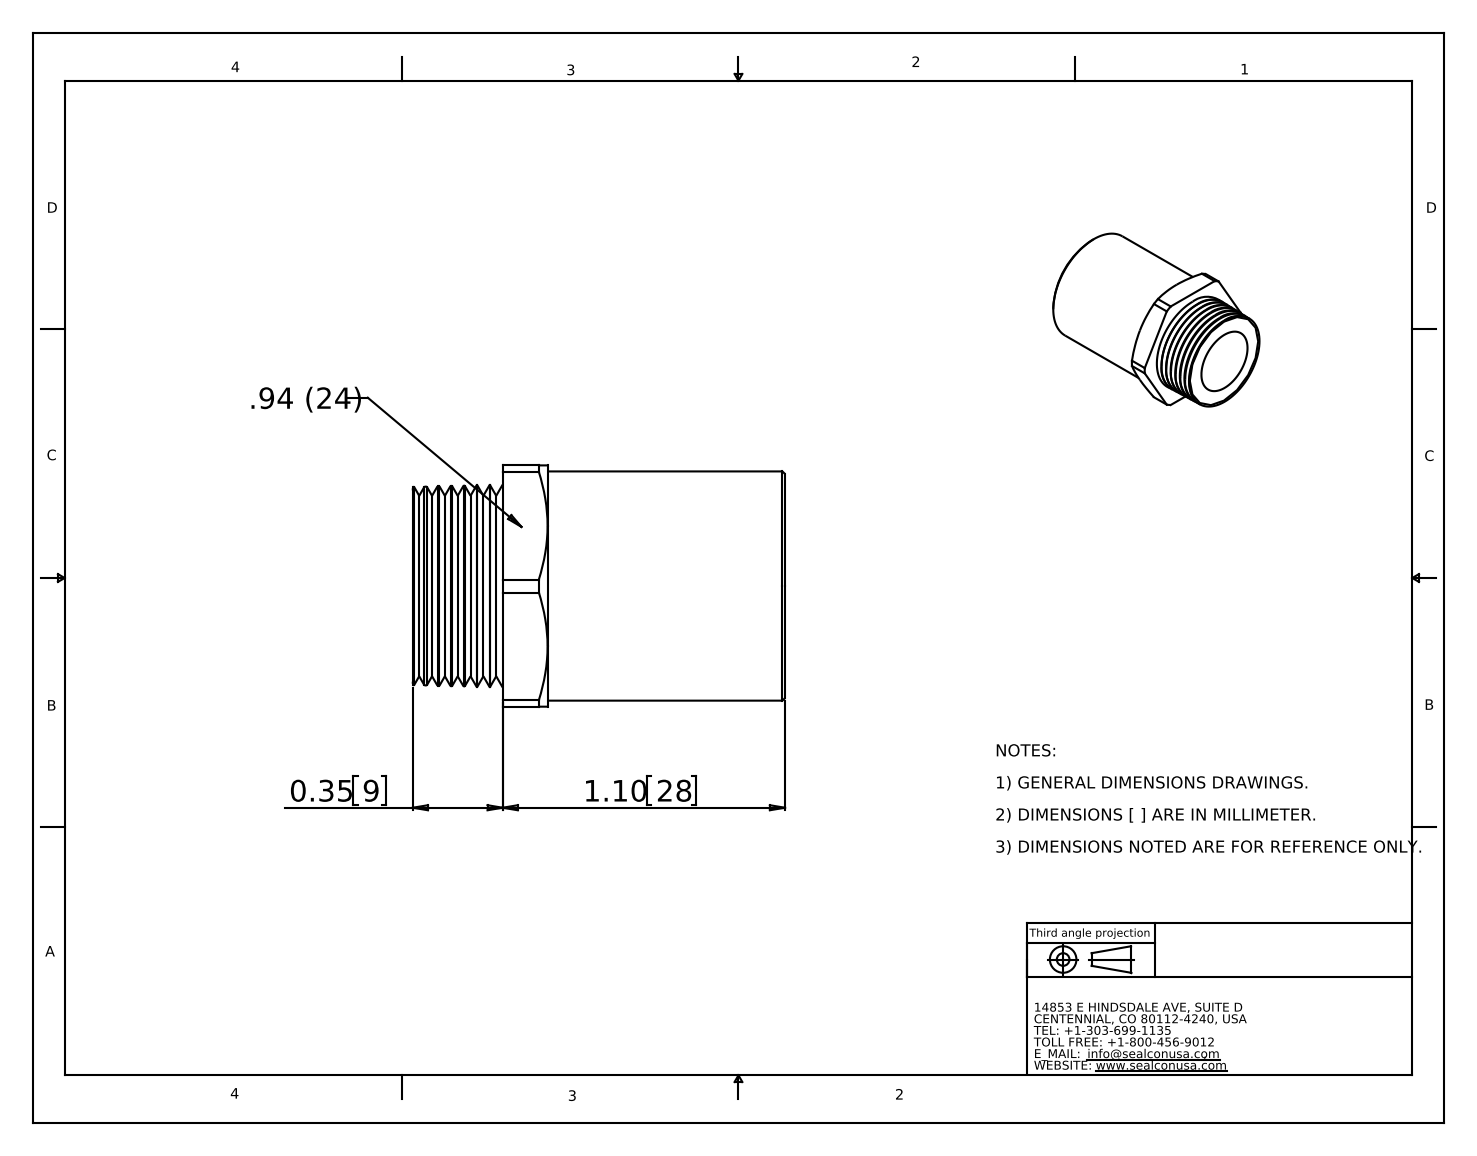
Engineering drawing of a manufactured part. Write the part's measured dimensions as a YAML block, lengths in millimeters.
part_name: "SM20MA-BK"
step_written_by: "SolidWorks 2007 (AUTOMOTIVE_DESIGN)"
units: millimeters
bodies: {solids: 1, faces: 75, planar: 11, cylindrical: 11, other: 53}
overall_size: [36.8, 26.9, 23.9]
volume: 5240
surface_area: 5734
round_holes:
  - {diameter: 20.1, count: 1}
round_bosses_or_shafts:
  - {diameter: 22.7, count: 1}
partial_cylinders:
  - {radius: 13.4, count: 1}
face_to_face_distances: [4.4, 13.3, 8.9, 23.9, 23.5, 27.9, 36.8]
